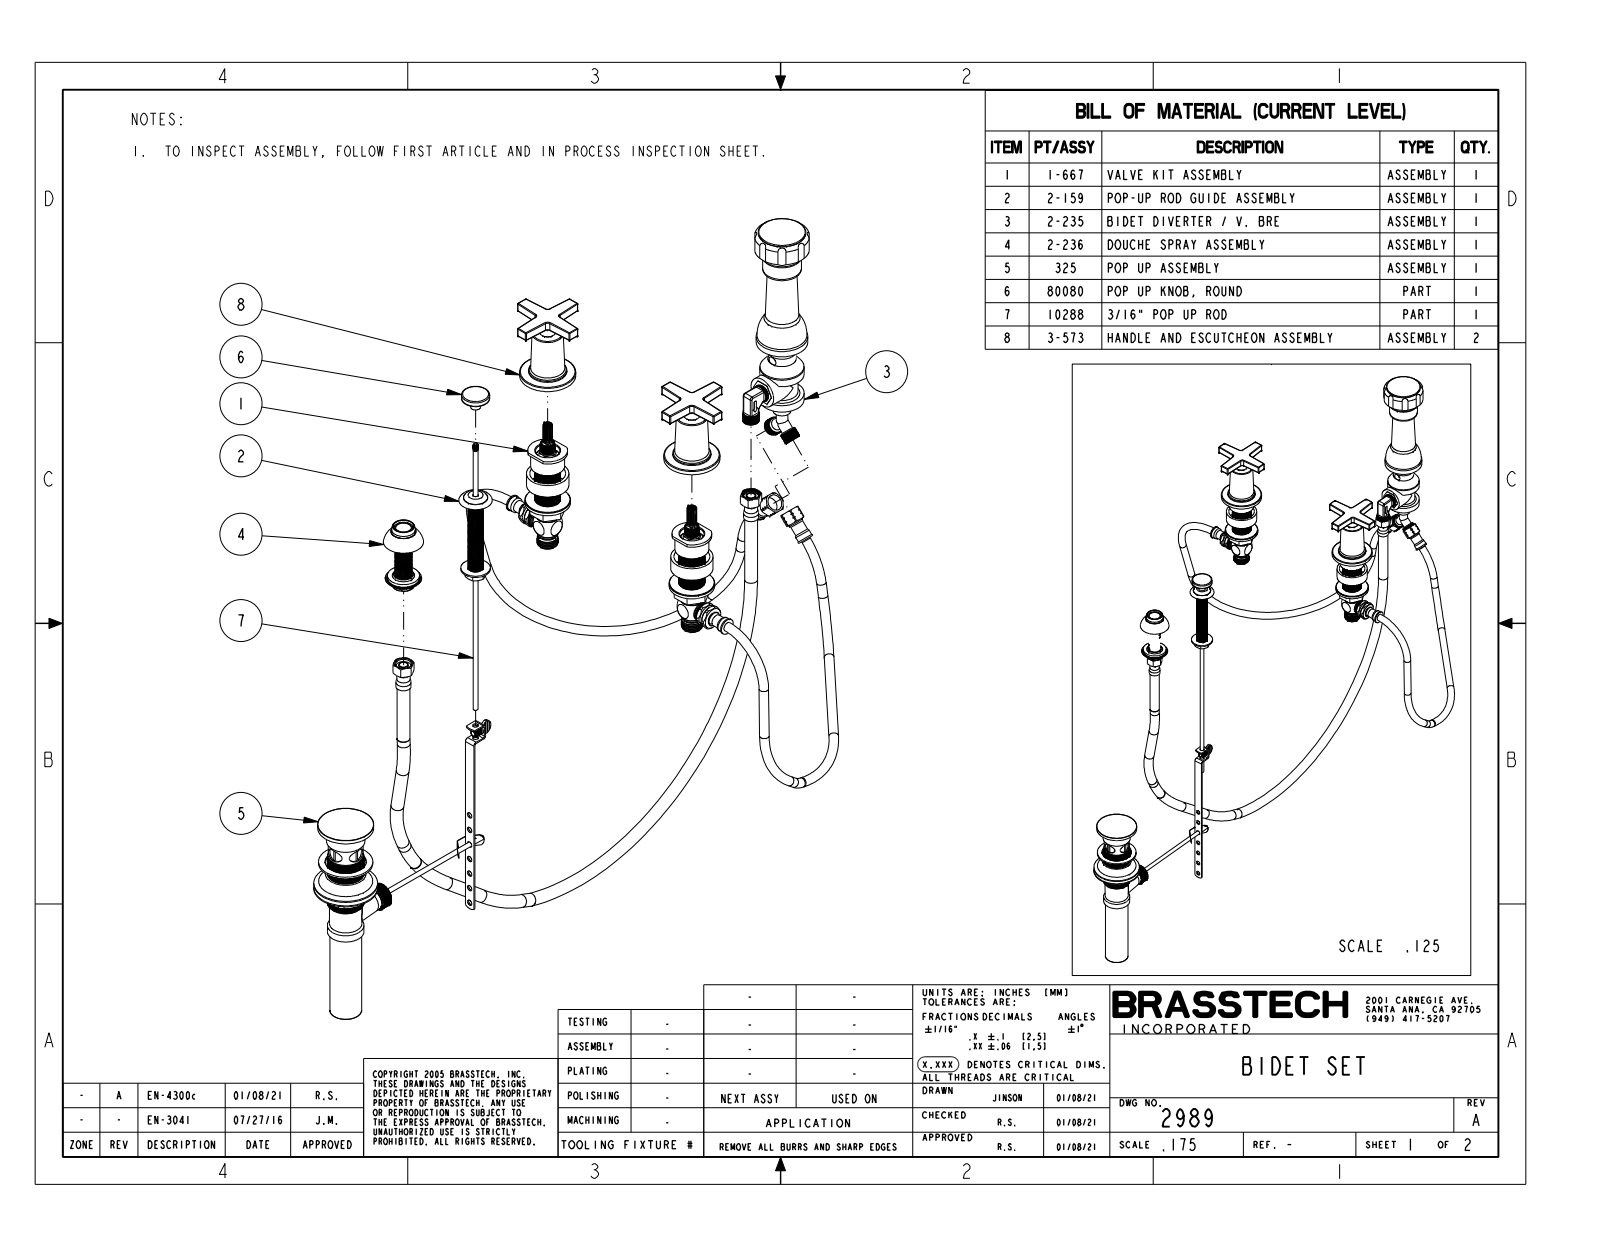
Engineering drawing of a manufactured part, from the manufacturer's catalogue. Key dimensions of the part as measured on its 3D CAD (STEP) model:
Part name (STEP PRODUCT): 2989
STEP written by: CREO PARAMETRIC BY PTC INC, 2018400 (CONFIG_CONTROL_DESIGN)
Units: inches
Bodies: 5 solids, 337 faces (79 planar, 138 cylindrical, 120 other)
Overall size (bounding box): 22.855 × 10.886 × 5.353
Volume: 20.91 in³ · Surface area: 103.8 in²
Round holes (diameter × count): ⌀1.3 ×2, ⌀0.625 ×1, ⌀0.792 ×1, ⌀0.94 ×1
Round bosses / shafts (diameter × count): ⌀2.2 ×2, ⌀1.5 ×2, ⌀1.275 ×2, ⌀0.625 ×2, ⌀0.525 ×2, ⌀2.025 ×1, ⌀1.52 ×1, ⌀1.1 ×1
Partial cylindrical surfaces — rounded edges, fillets, slot ends (radius × count): R0.03 ×60, R0.125 ×8, R0.21 ×8, R0.357 ×1, R1.077 ×1
Main face-to-face distances: 2.87, 0.187, 2.683, 0.375, 2.495, 2.308, 2.047, 1.86, 0.448, 0.823
Hole centre spacings: 12.649, 8
